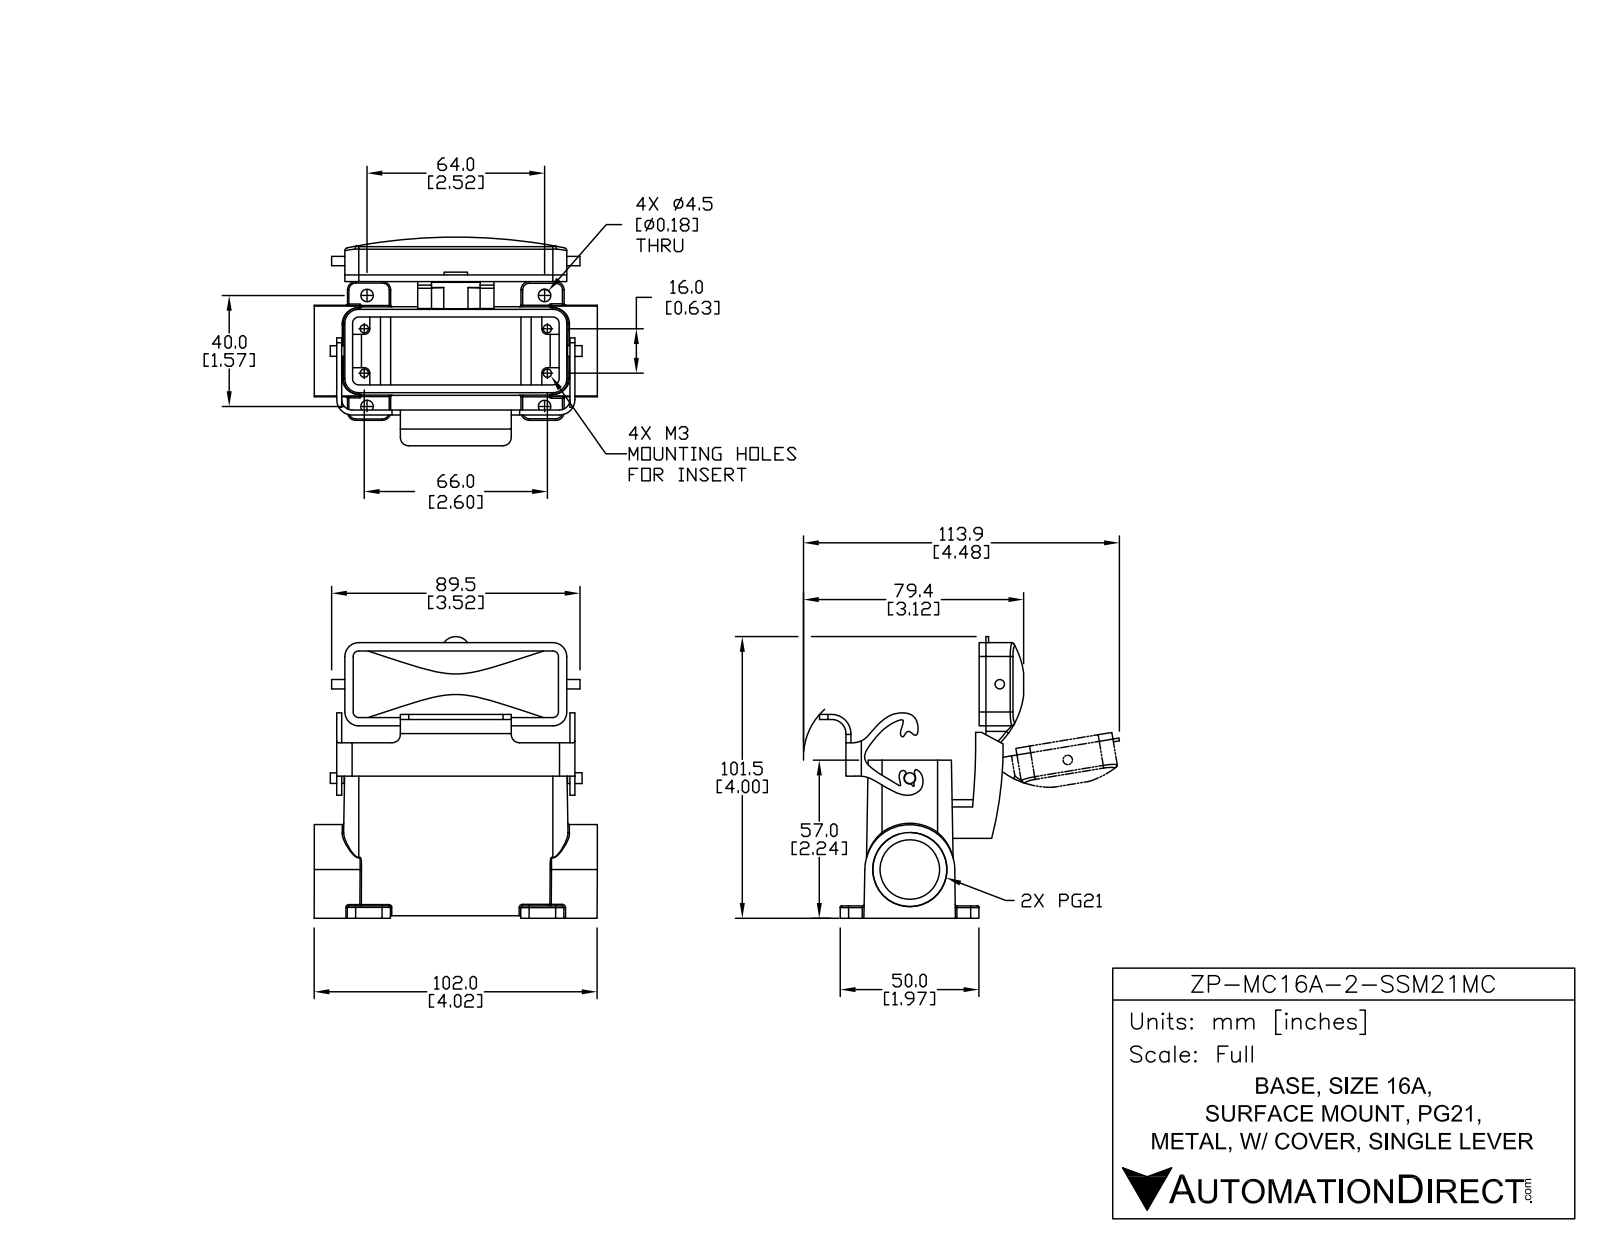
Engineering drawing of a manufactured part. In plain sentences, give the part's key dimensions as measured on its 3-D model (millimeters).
The part is named "ZP-MC16A-2-SSM21MC". Its 3-D file was written by "SolidWorks 2014 (AUTOMOTIVE_DESIGN)". It is 7 solids with 414 faces: 159 planar, 173 cylindrical and 82 other. Overall it measures 102 by 101.44 by 75.2 millimeters. Its volume is 83 852 cubic millimeters and its surface area 57 392 square millimeters. Round holes: 4 of diameter 3, 4 of diameter 4.5, 1 of diameter 21.25, 1 of diameter 26.75. Round bosses or shafts: 1 of diameter 7.5, 1 of diameter 3.9, 1 of diameter 3.8. Partial cylindrical surfaces (rounded edges, fillets, slot ends): 18 of radius 0.5, 13 of radius 0.6, 12 of radius 3, 10 of radius 2, 8 of radius 5, 4 of radius 1, 2 of radius 3.75, 2 of radius 5.55. The main face-to-face distances are 2.77, 3, 4.44, 0.52, 1.8, 94.83, 0.92, 3.52, 1.44, 67.83. The hole center spacings are 12.04, 28.02, 66.1, 70.77, 16, 40, 64, 66.
